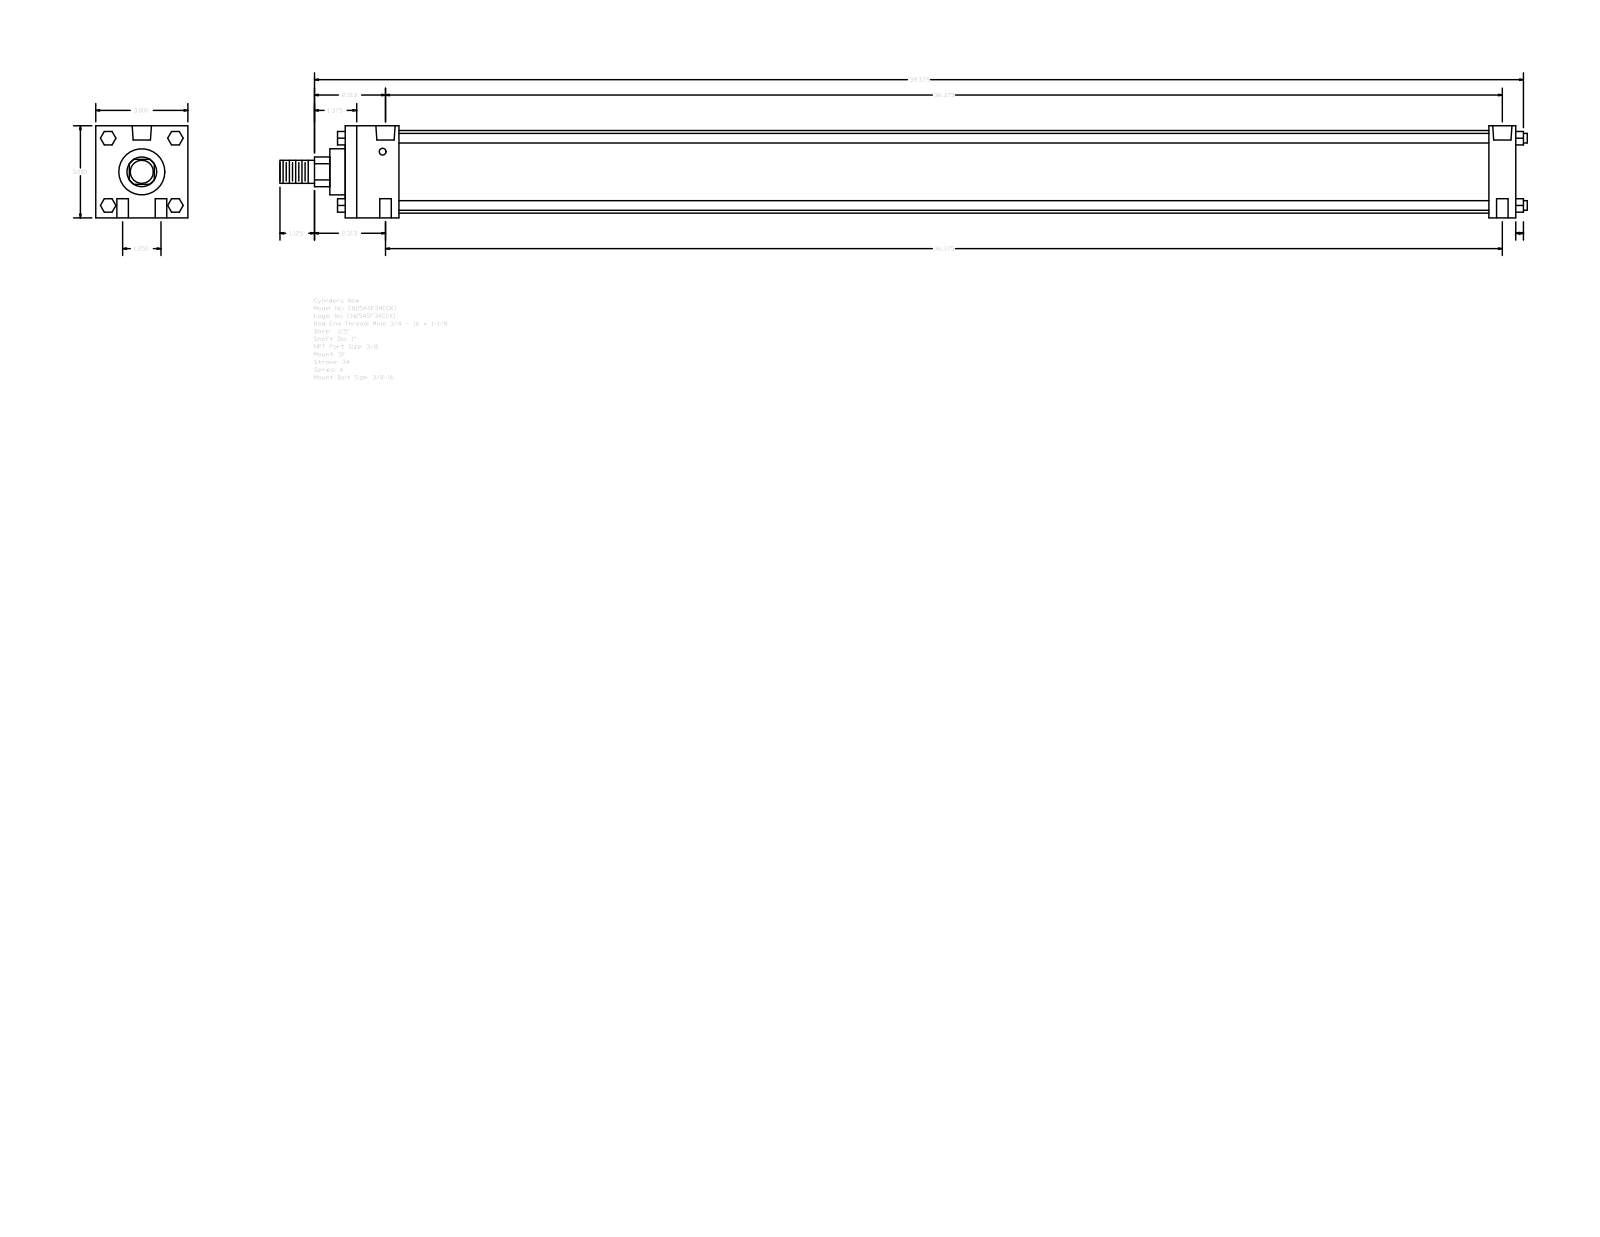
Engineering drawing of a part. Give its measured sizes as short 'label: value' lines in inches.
name: A_SF__0250_1
written by: GSSL Pune (CONFIG_CONTROL_DESIGN)
unit: in
bodies: 0 solids, 124 faces (94 planar, 30 cylindrical, 0 other)
size: 40.625 × 3 × 3
holes: 4× ⌀0.375, 2× ⌀0.219, 2× ⌀0.627
bosses: 4× ⌀0.313, 1× ⌀2.69, 1× ⌀1.5, 1× ⌀1, 1× ⌀0.75
rounds: 1× R0.484
face distances: 3, 38.125, 37.25, 0.875, 1.75, 35.5, 36.375, 0.5, 38.625, 0.25
hole spacings: 0.625, 36.38, 36.375, 1.25, 36.396, 36.562
